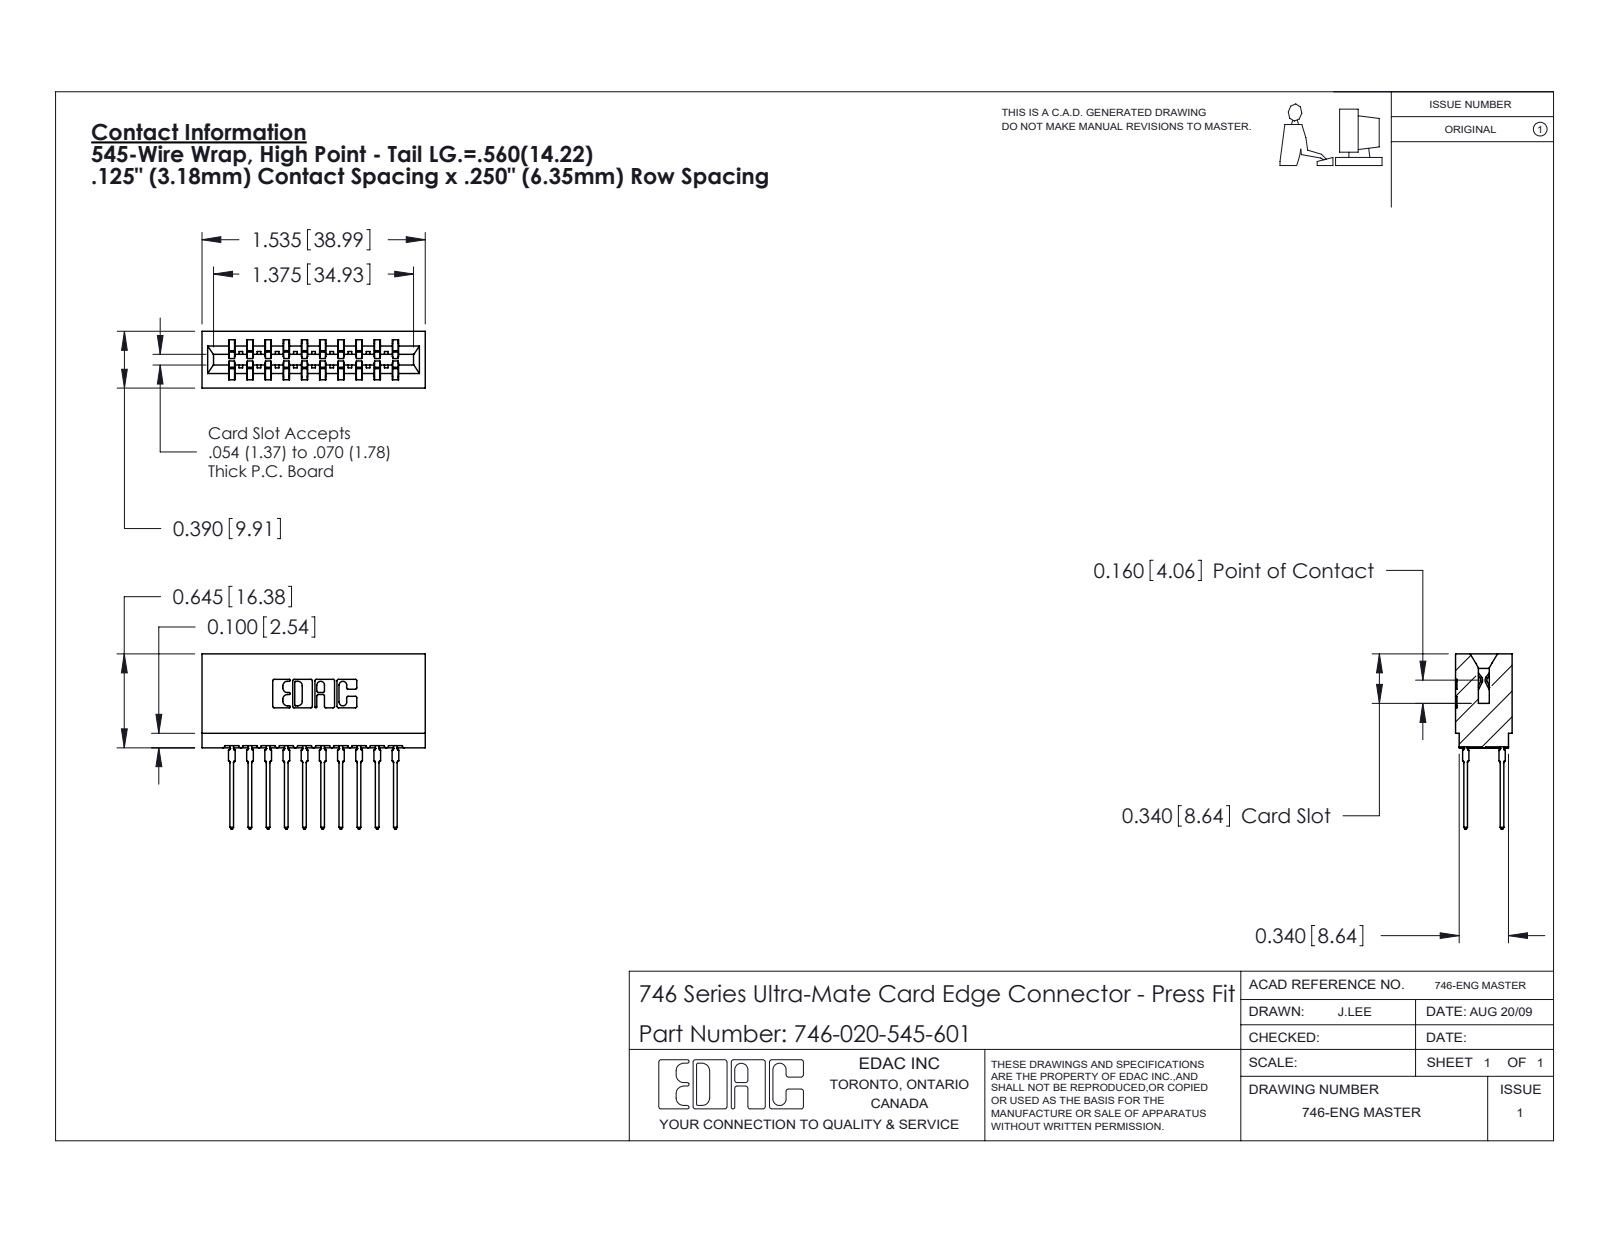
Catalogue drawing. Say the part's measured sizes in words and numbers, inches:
The part is named "746-292-001_545; 746 Part_.340 Slot Depth - 01; 746-020-545-601". Its 3-D file was written by "SolidWorks 2020 (CONFIG_CONTROL_DESIGN)". It is 21 solids with 1887 faces: 975 planar, 392 cylindrical and 520 other. Overall it measures 1.535 by 1.204 by 0.39 inches. Its volume is 0.289 cubic inches and its surface area 10.36 square inches. Partial cylindrical surfaces (rounded edges, fillets, slot ends): 40 of radius 0.021, 22 of radius 0.01, 11 of radius 0.015, 8 of radius 0.005, 8 of radius 0.011, 6 of radius 0.007, 6 of radius 0.031, 3 of radius 0.026. The main face-to-face distances are 0.25, 0.057, 0.333, 0.5, 0.042, 0.125, 0.292, 0.375, 0.125, 0.083.
